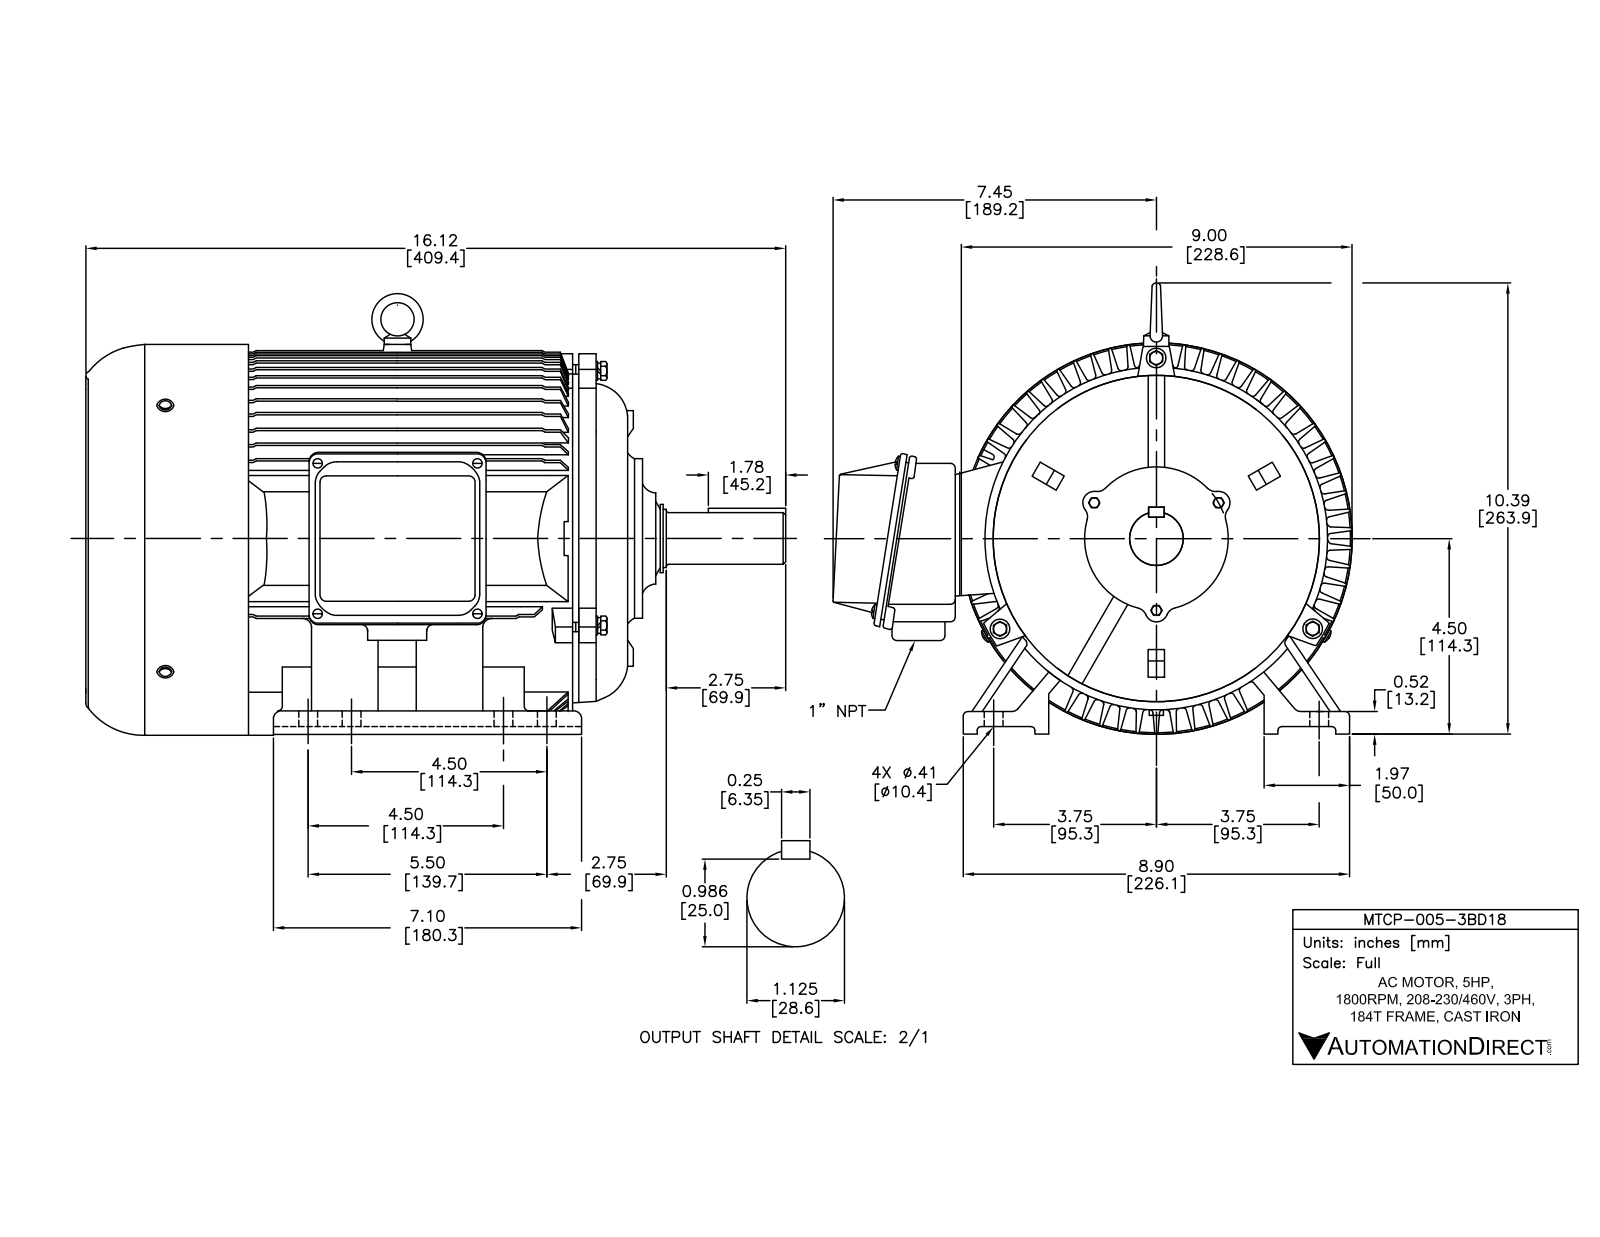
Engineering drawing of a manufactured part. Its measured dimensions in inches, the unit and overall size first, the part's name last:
Units: inches
Overall size (bounding box): 348.417 × 339.438 × 324.546
Round holes (diameter × count): ⌀5 ×23, ⌀3.558 ×22, ⌀5.625 ×19, ⌀5.625 ×16, ⌀29.25 ×9, ⌀4.003 ×6, ⌀4.613 ×6, ⌀6.75 ×6, ⌀8.48 ×6, ⌀10 ×6, ⌀10.4 ×5, ⌀26.817 ×5
Round bosses / shafts (diameter × count): ⌀8 ×109, ⌀5.693 ×88, ⌀5 ×18, ⌀3.417 ×18, ⌀6.27 ×13, ⌀16 ×6, ⌀10 ×6, ⌀192 ×2
Partial cylindrical surfaces — rounded edges, fillets, slot ends (radius × count): R0.5 ×656, R3 ×114, R1.5 ×40, R1.25 ×34, R3.375 ×33, R0.625 ×24, R0.312 ×12, R2.25 ×8
Main face-to-face distances: 188.985, 23.004, 211.989, 26.002, 214.988, 237.991, 2.999, 234.993, 59.302, 303.284
Hole centre spacings: 110.25, 149.689, 110.25, 149.688, 98, 101.25, 101.25, 98
Bodies: 0 solids, 4813 faces (1195 planar, 2322 cylindrical, 1296 other)
Part name (STEP PRODUCT): MTCP-005-3BD18
STEP written by: SolidWorks 2017 (AUTOMOTIVE_DESIGN)
